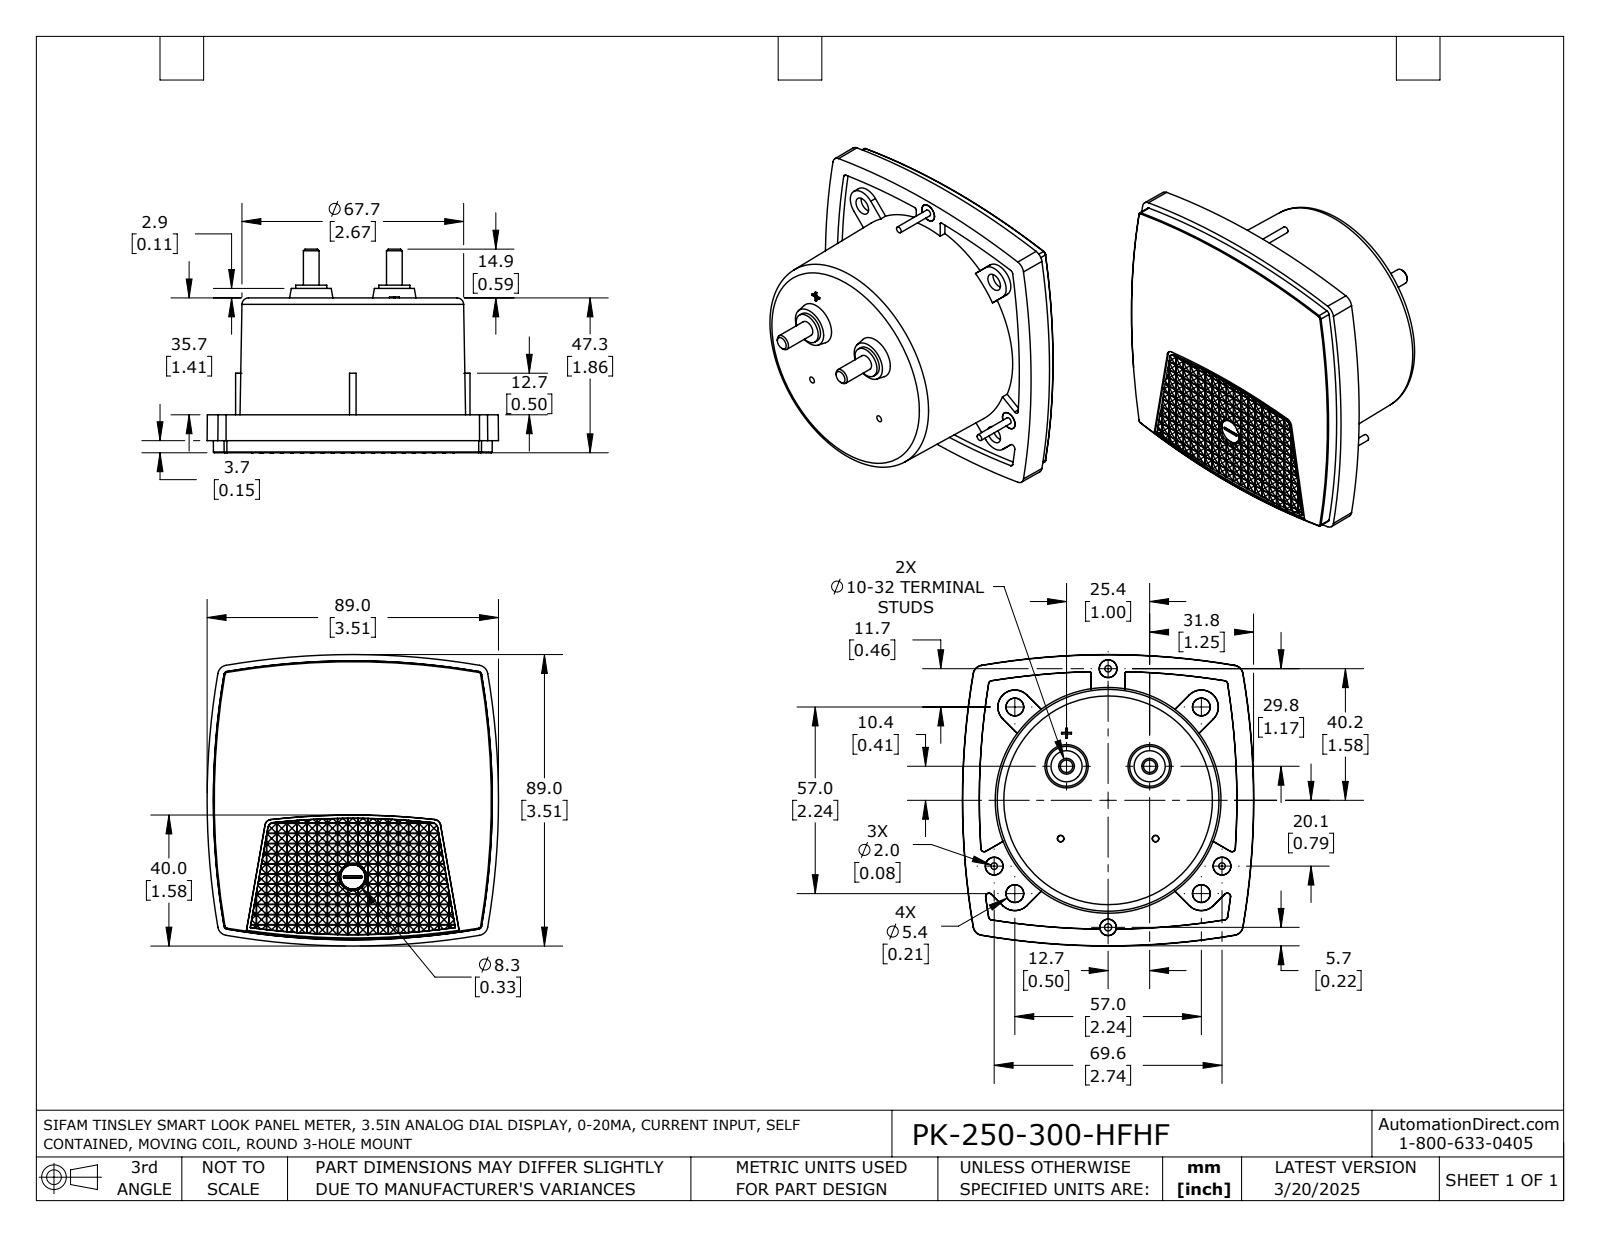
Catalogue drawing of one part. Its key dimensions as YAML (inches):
part_name: "PK-250-300-HFHF"
step_written_by: "SolidWorks 2021 (AUTOMOTIVE_DESIGN)"
units: inches
bodies: {solids: 1, faces: 1078, planar: 950, cylindrical: 23, other: 105}
overall_size: [3.505, 3.505, 2.453]
volume: 12.99
surface_area: 44.29
round_holes:
  - {diameter: 0.087, count: 1}
round_bosses_or_shafts:
  - {diameter: 0.213, count: 3}
  - {diameter: 0.079, count: 3}
  - {diameter: 0.374, count: 2}
  - {diameter: 0.189, count: 2}
partial_cylinders:
  - {radius: 8.961, count: 1}
face_to_face_distances: [1.862, 1.406, 0.457, 0.079, 1.484, 0.378, 0.024, 0.096, 0.072, 0.12]
